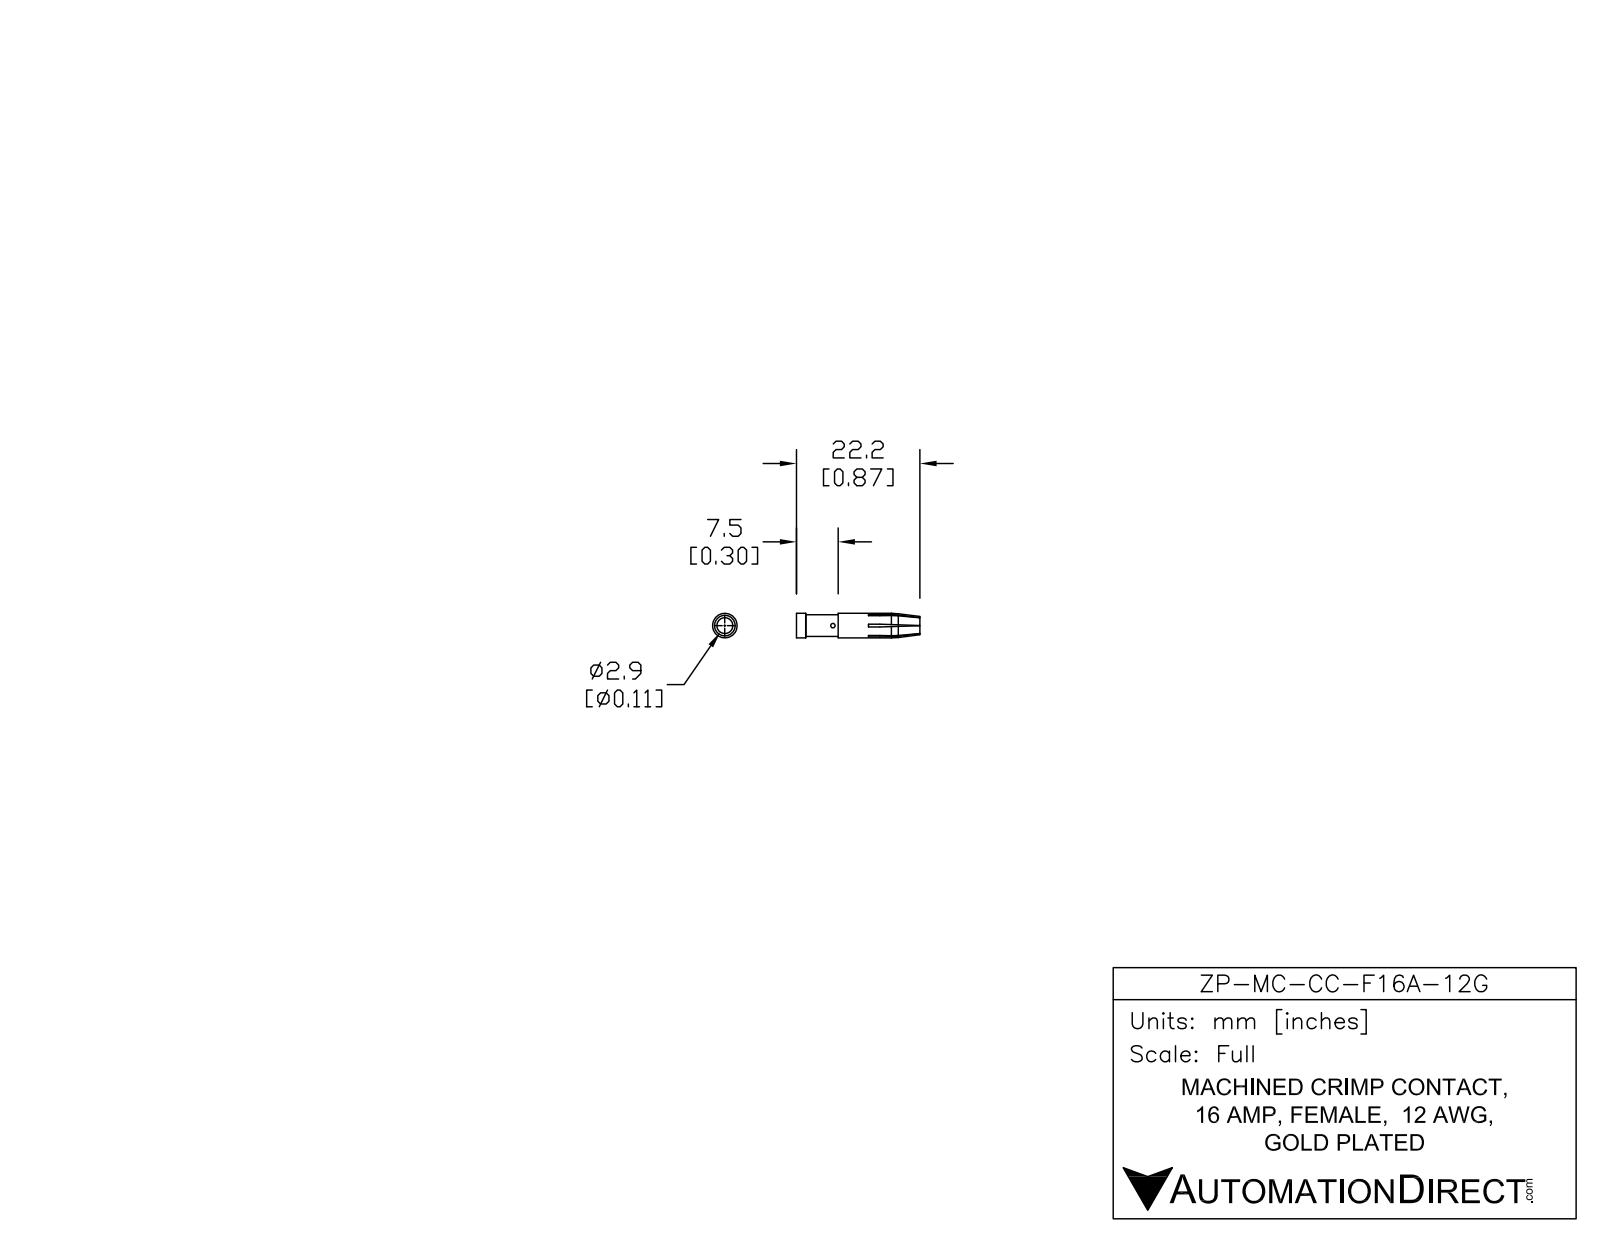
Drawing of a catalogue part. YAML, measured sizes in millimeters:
part_name: "ZP-MC-CC-F16A-12G"
step_written_by: "SolidWorks 2014 (AUTOMOTIVE_DESIGN)"
units: millimeters
bodies: {solids: 1, faces: 68, planar: 34, cylindrical: 10, other: 24}
overall_size: [22.2, 4.42, 4.42]
volume: 184
surface_area: 522
round_holes:
  - {diameter: 0.8, count: 1}
  - {diameter: 2.85, count: 1}
round_bosses_or_shafts:
  - {diameter: 4.42, count: 1}
  - {diameter: 3.9, count: 1}
face_to_face_distances: [0.5, 7.5, 14.7, 22.2, 9.25, 5.45, 12.95]
